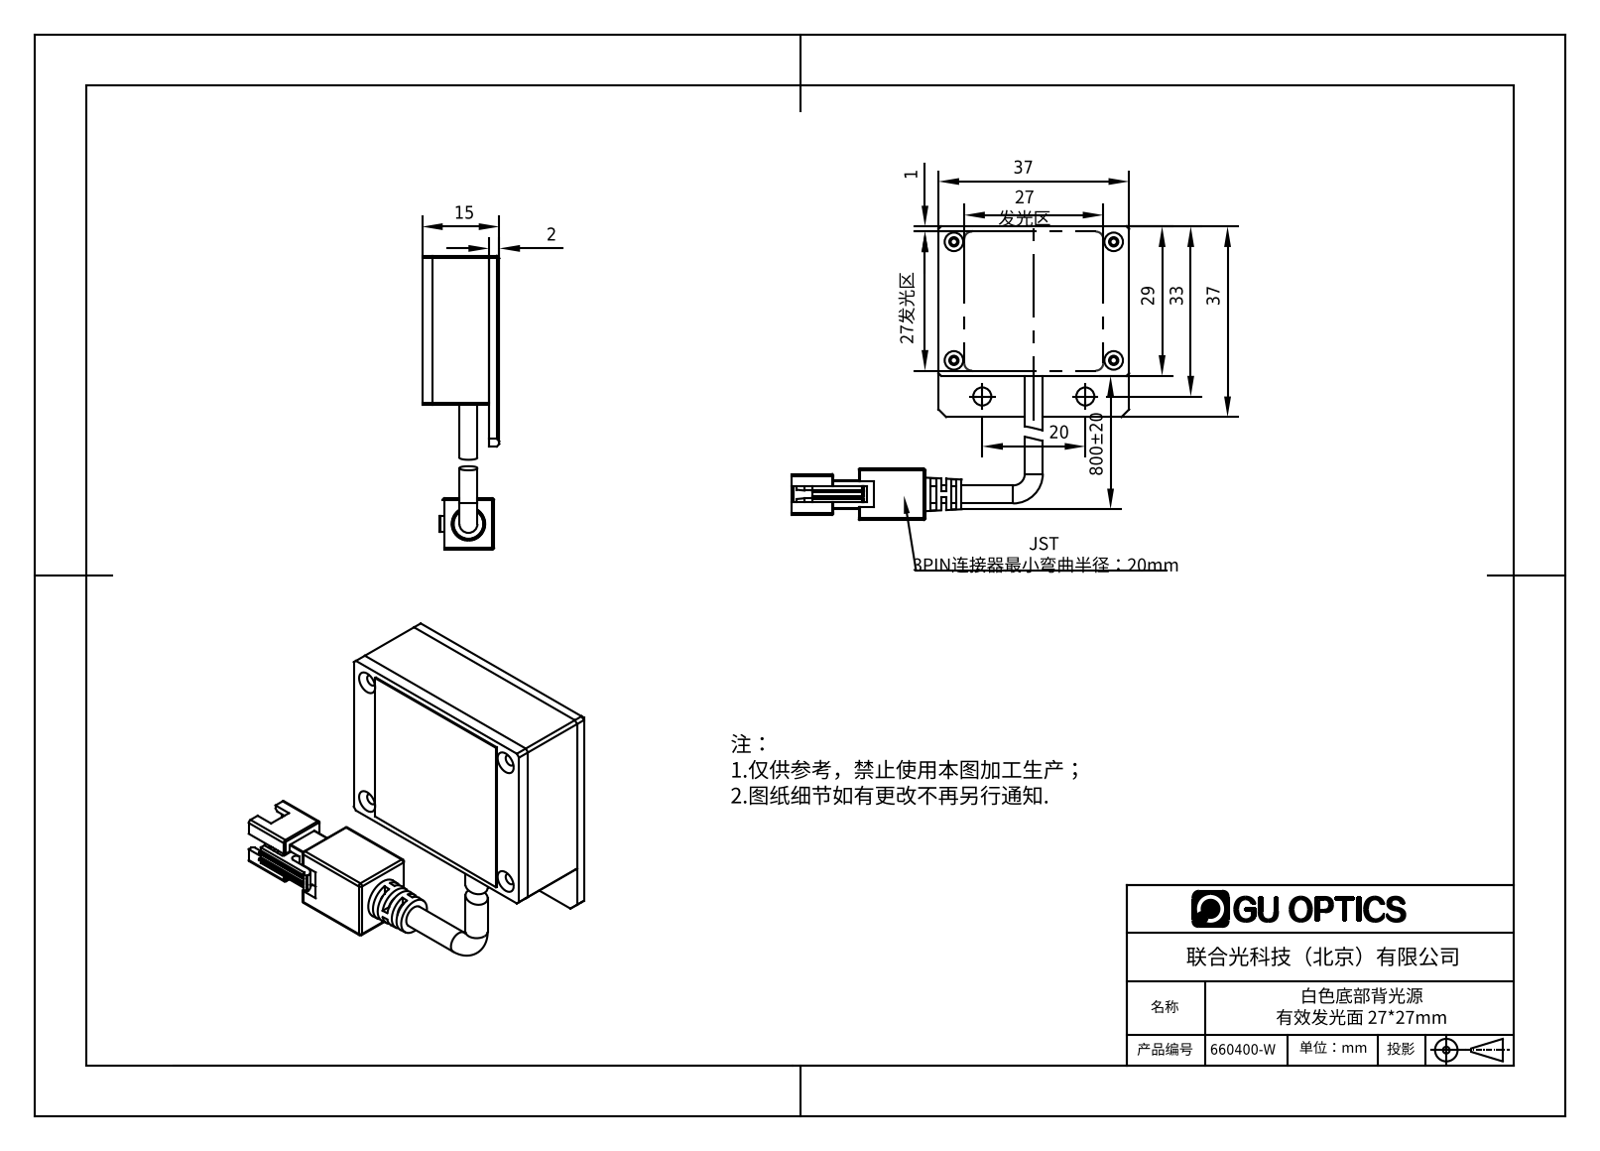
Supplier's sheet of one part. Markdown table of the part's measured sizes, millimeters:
| quantity | value |
| --- | --- |
| part name | 660400-W |
| STEP written by | SolidWorks 2016 (AUTOMOTIVE_DESIGN) |
| units | millimeters |
| bodies | 6 solids, 616 faces (375 planar, 122 cylindrical, 119 other) |
| overall size | 65.5 × 57 × 15.2 |
| volume | 11 682 mm³ |
| surface area | 12 966 mm² |
| round holes (diameter × count) | 1.25 × 4, 1.6 × 4, 1.8 × 4, 2 × 4, 2.4 × 4, 3.5 × 2 |
| round bosses / shafts (diameter × count) | 3.5 × 2 |
| partial cylindrical surfaces (radius × count) | 0.1 × 15, 0.2 × 13, 0.4 × 12, 1 × 4, 1.5 × 4, 0.75 × 2, 0.8 × 2, 0.3 × 1 |
| main face-to-face distances | 2, 1, 11, 13, 2.3, 10.7, 1.3, 28, 2.2, 15.2 |
| hole center spacings | 8.9, 23, 26.44, 30.5, 31, 38.6, 39.37, 20 |
